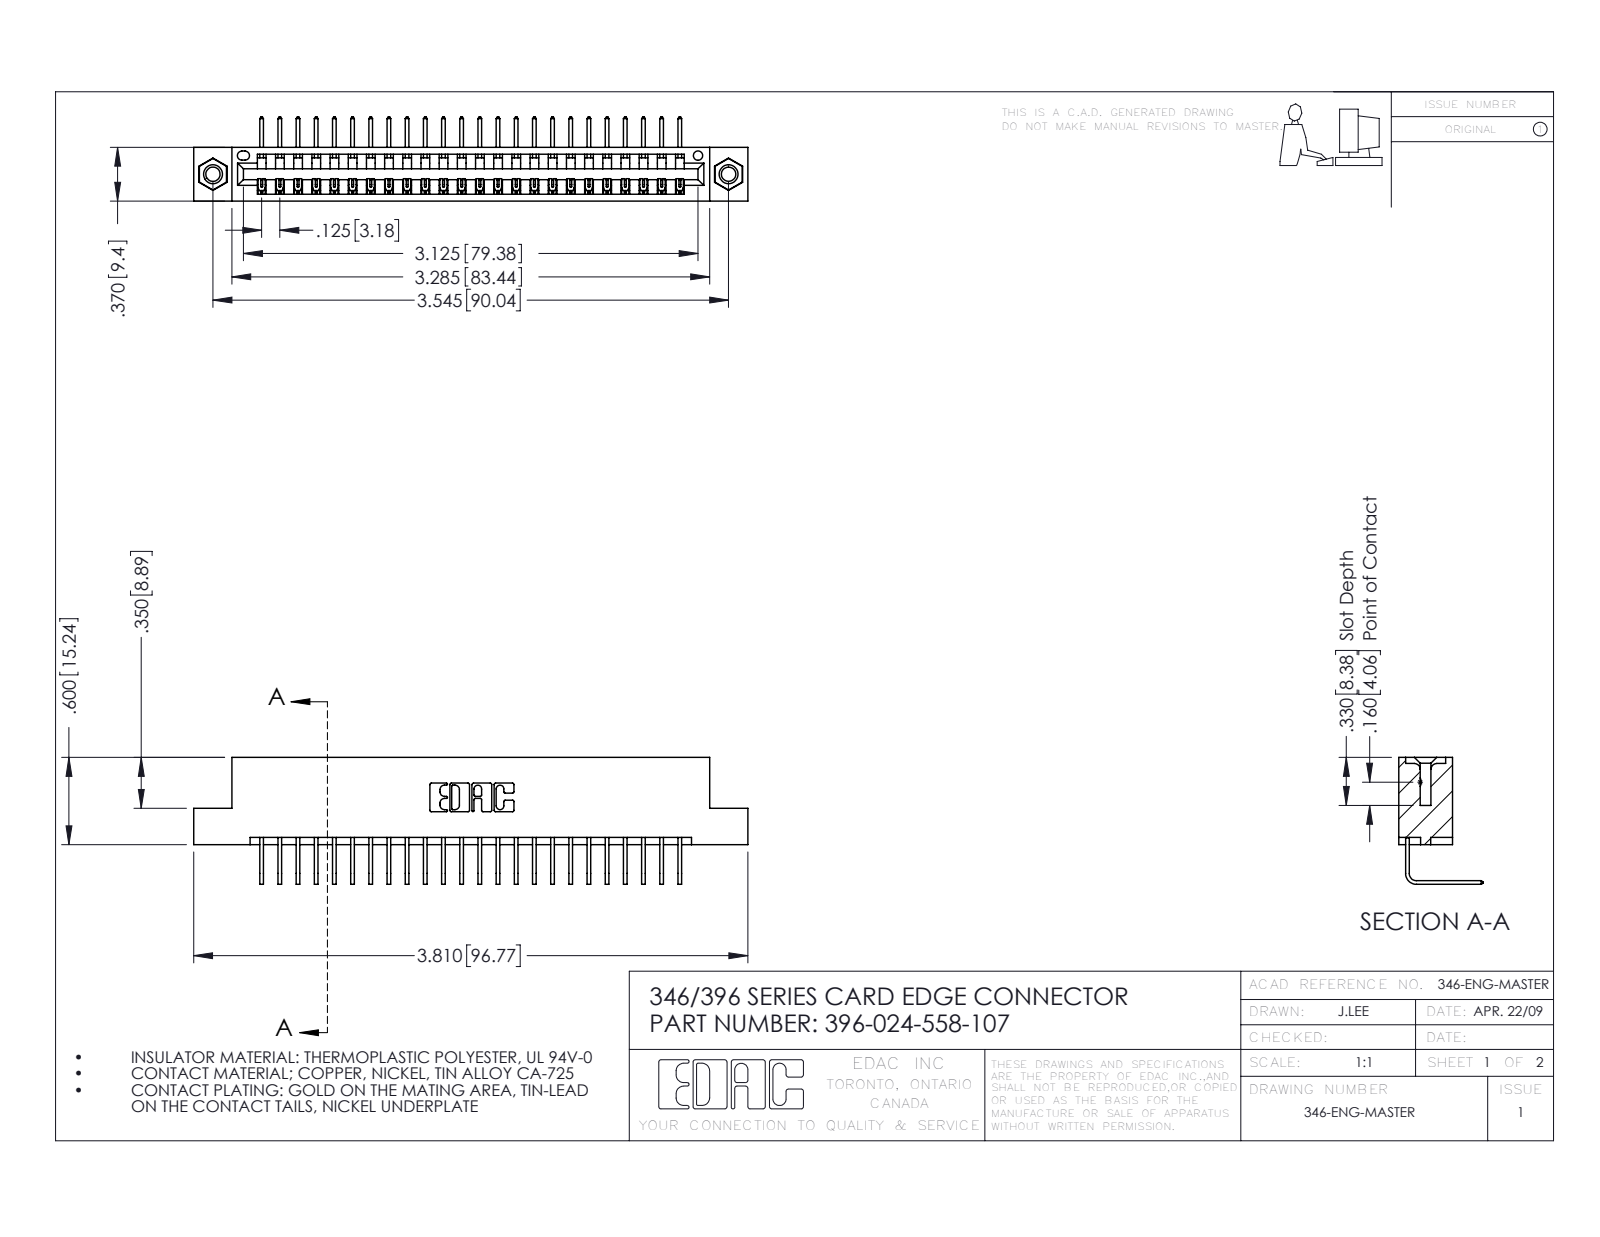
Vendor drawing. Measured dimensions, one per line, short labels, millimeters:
name: 345-250-001_345-250-005-103; 396-024-558-107; 346 Part_Flush Mounting Lugs - 0.156 Dia-TI; 345-292-001_558 Tail - 2
written by: SolidWorks 2016 (CONFIG_CONTROL_DESIGN)
unit: mm
bodies: 27 solids, 1622 faces (1116 planar, 490 cylindrical, 16 other)
size: 96.8 × 22.2 × 14.7
volume: 9 210 mm³; area: 11 830 mm²
holes: 2× ⌀2.5, 2× ⌀3.2, 2× ⌀4, 1× ⌀1.6
bosses: 2× ⌀3.9
rounds: 48× R0.2, 22× R0.3, 6× R0.2, 6× R0.8, 3× R0.7, 2× R0.8, 2× R1, 1× R0.4
face distances: 8.2, 1.2, 9.4, 6.4, 7.6, 0.6, 1.8, 3.8, 5.6, 2.5
hole spacings: 6.2, 84.8, 90
